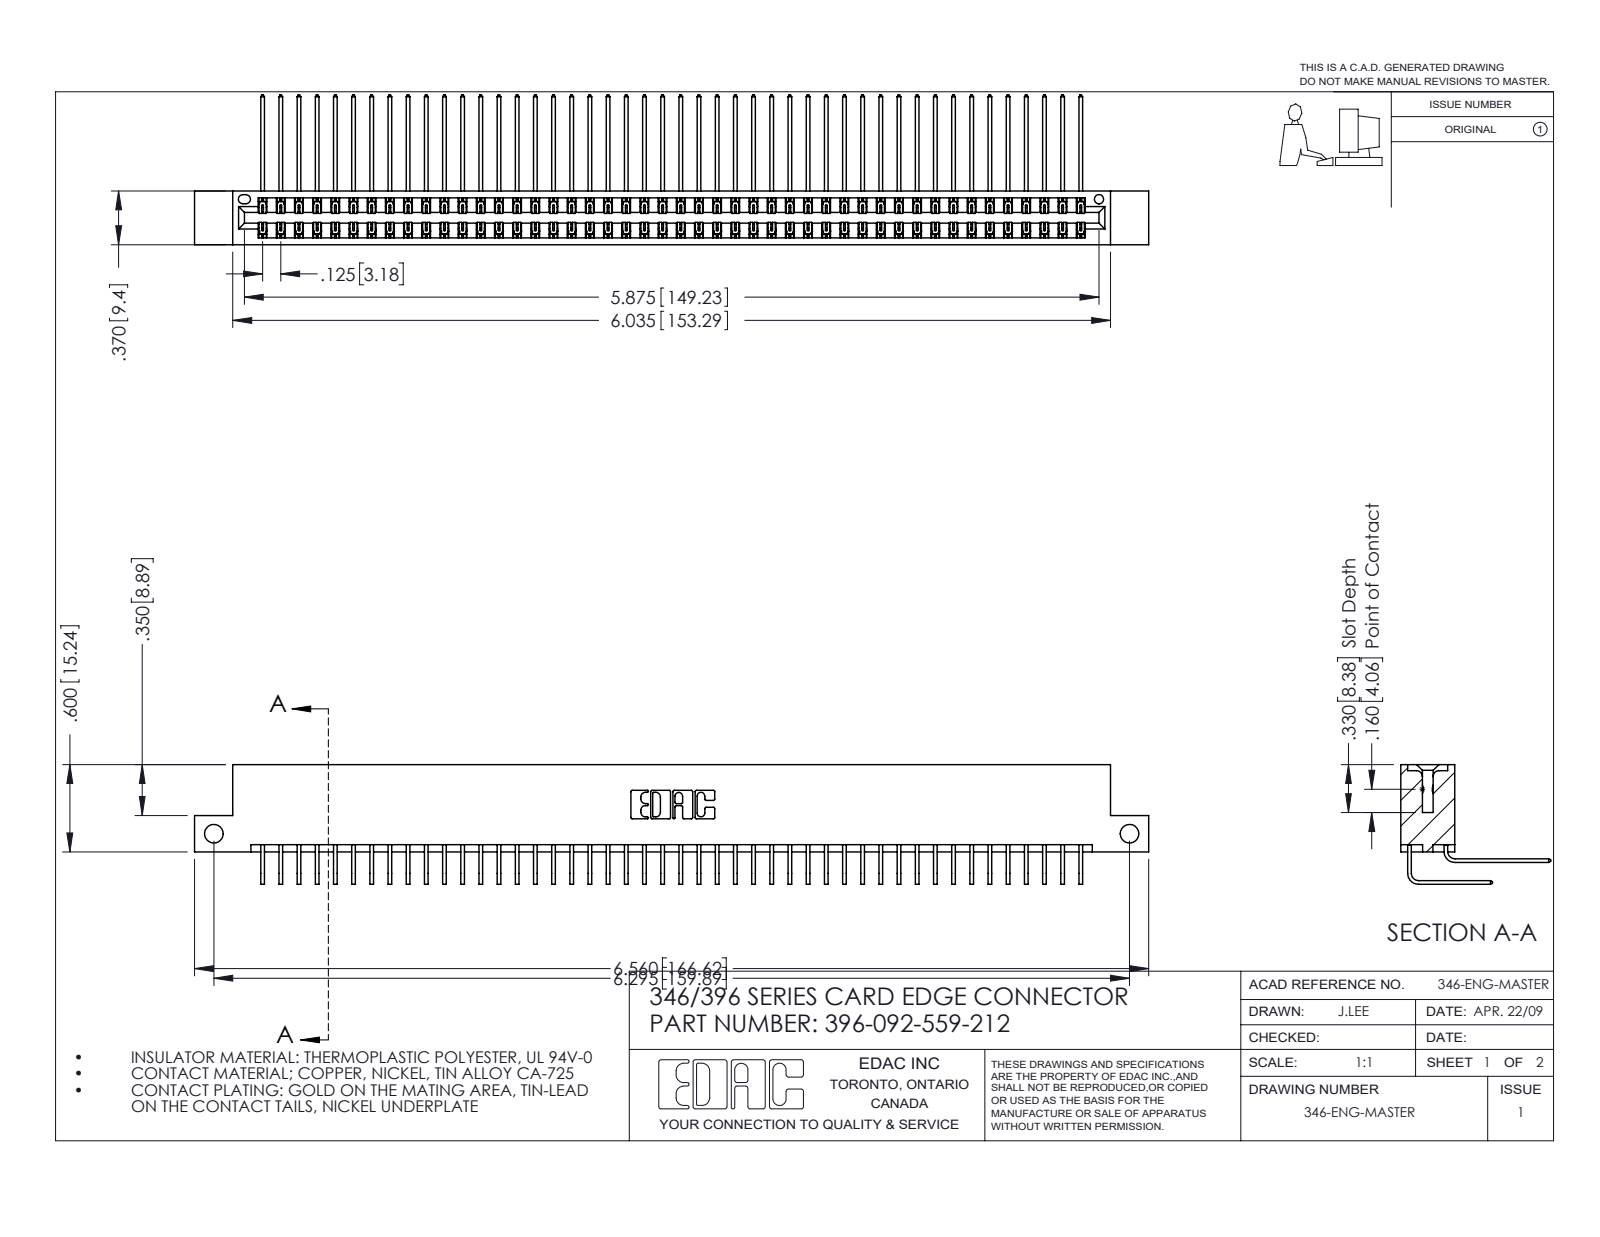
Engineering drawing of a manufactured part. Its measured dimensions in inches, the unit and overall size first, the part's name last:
Units: inches
Overall size (bounding box): 6.56 × 1.03 × 0.823
Round holes (diameter × count): ⌀0.128 ×2, ⌀0.064 ×1
Partial cylindrical surfaces — rounded edges, fillets, slot ends (radius × count): R0.006 ×138, R0.01 ×22, R0.007 ×6, R0.031 ×6, R0.026 ×3, R0.014 ×2, R0.022 ×2, R0.024 ×2
Main face-to-face distances: 0.048, 0.322, 0.025, 0.37, 0.25, 0.072, 0.298, 0.275, 0.148, 0.222
Hole centre spacings: 6.295
Volume: 1.02 in³ · Surface area: 39.46 in²
Bodies: 93 solids, 5090 faces (3480 planar, 1610 cylindrical, 0 other)
Part name (STEP PRODUCT): 345-292-001_559 Tail - 2; 396-092-559-212; 345-292-001_558 559 Tail - 1; 346 Part_Flush Mounting Lugs - Side Mount
STEP written by: SolidWorks 2016 (CONFIG_CONTROL_DESIGN)
